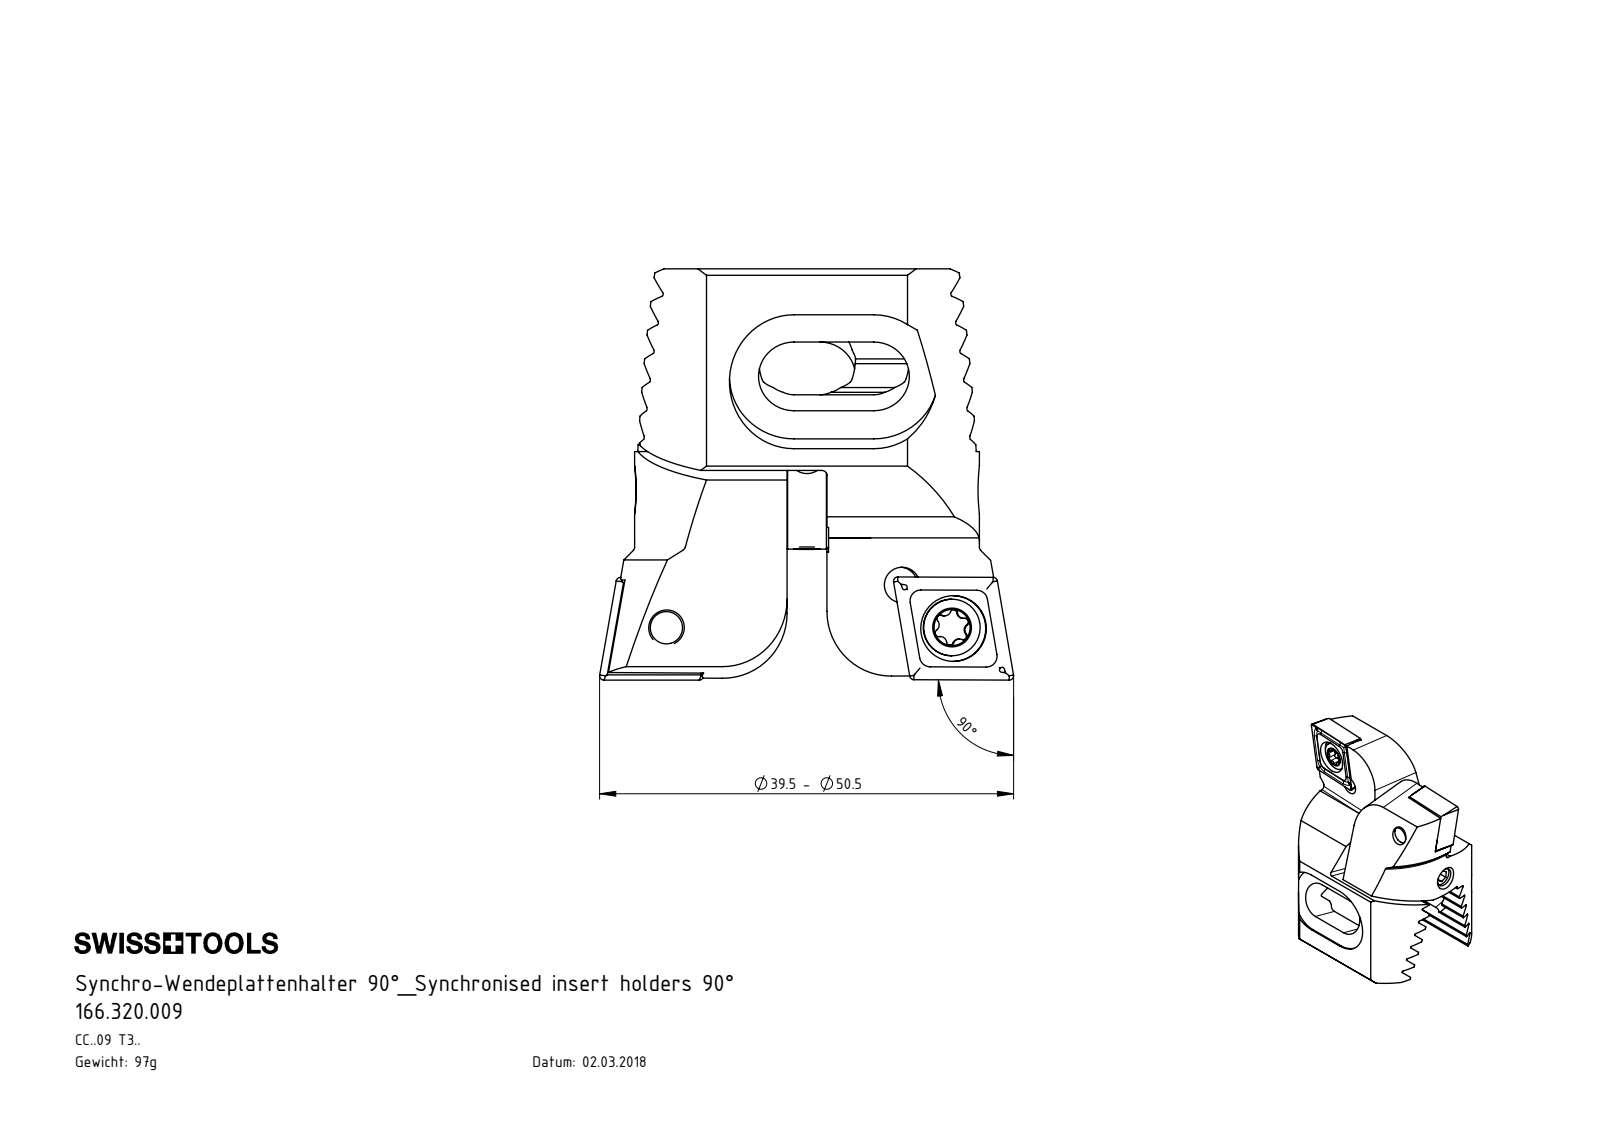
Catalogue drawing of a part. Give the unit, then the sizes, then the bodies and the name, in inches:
Units: inches
Overall size (bounding box): 1.513 × 1.502 × 1.031
Round holes (diameter × count): ⌀0.13 ×4, ⌀0.039 ×3, ⌀0.098 ×3, ⌀0.173 ×2, ⌀0.24 ×2, ⌀0.138 ×1
Round bosses / shafts (diameter × count): ⌀0.118 ×4, ⌀0.157 ×3, ⌀0.207 ×2, ⌀0.433 ×1
Partial cylindrical surfaces — rounded edges, fillets, slot ends (radius × count): R0.008 ×12, R0.013 ×12, R0.023 ×12, R0.039 ×8, R0.236 ×6, R0.02 ×4, R0.13 ×4, R0.63 ×2
Main face-to-face distances: 0.094, 0.375, 0.281, 0.187, 0.469, 0.152, 0.188, 0.032, 0.161, 0.379
Hole centre spacings: 0.394, 1.066, 0.079, 0.24, 0.24, 0.246, 0.246, 0.402
Volume: 0.754 in³ · Surface area: 13.74 in²
Bodies: 11 solids, 503 faces (193 planar, 158 cylindrical, 152 other)
Part name (STEP PRODUCT): 166.320.009; Z25-ER3.002.004_B; Z32-ER3.001.030_A; WCB-ER2.001.009_A (+4 more)
STEP written by: SolidWorks 2017 (CONFIG_CONTROL_DESIGN)
